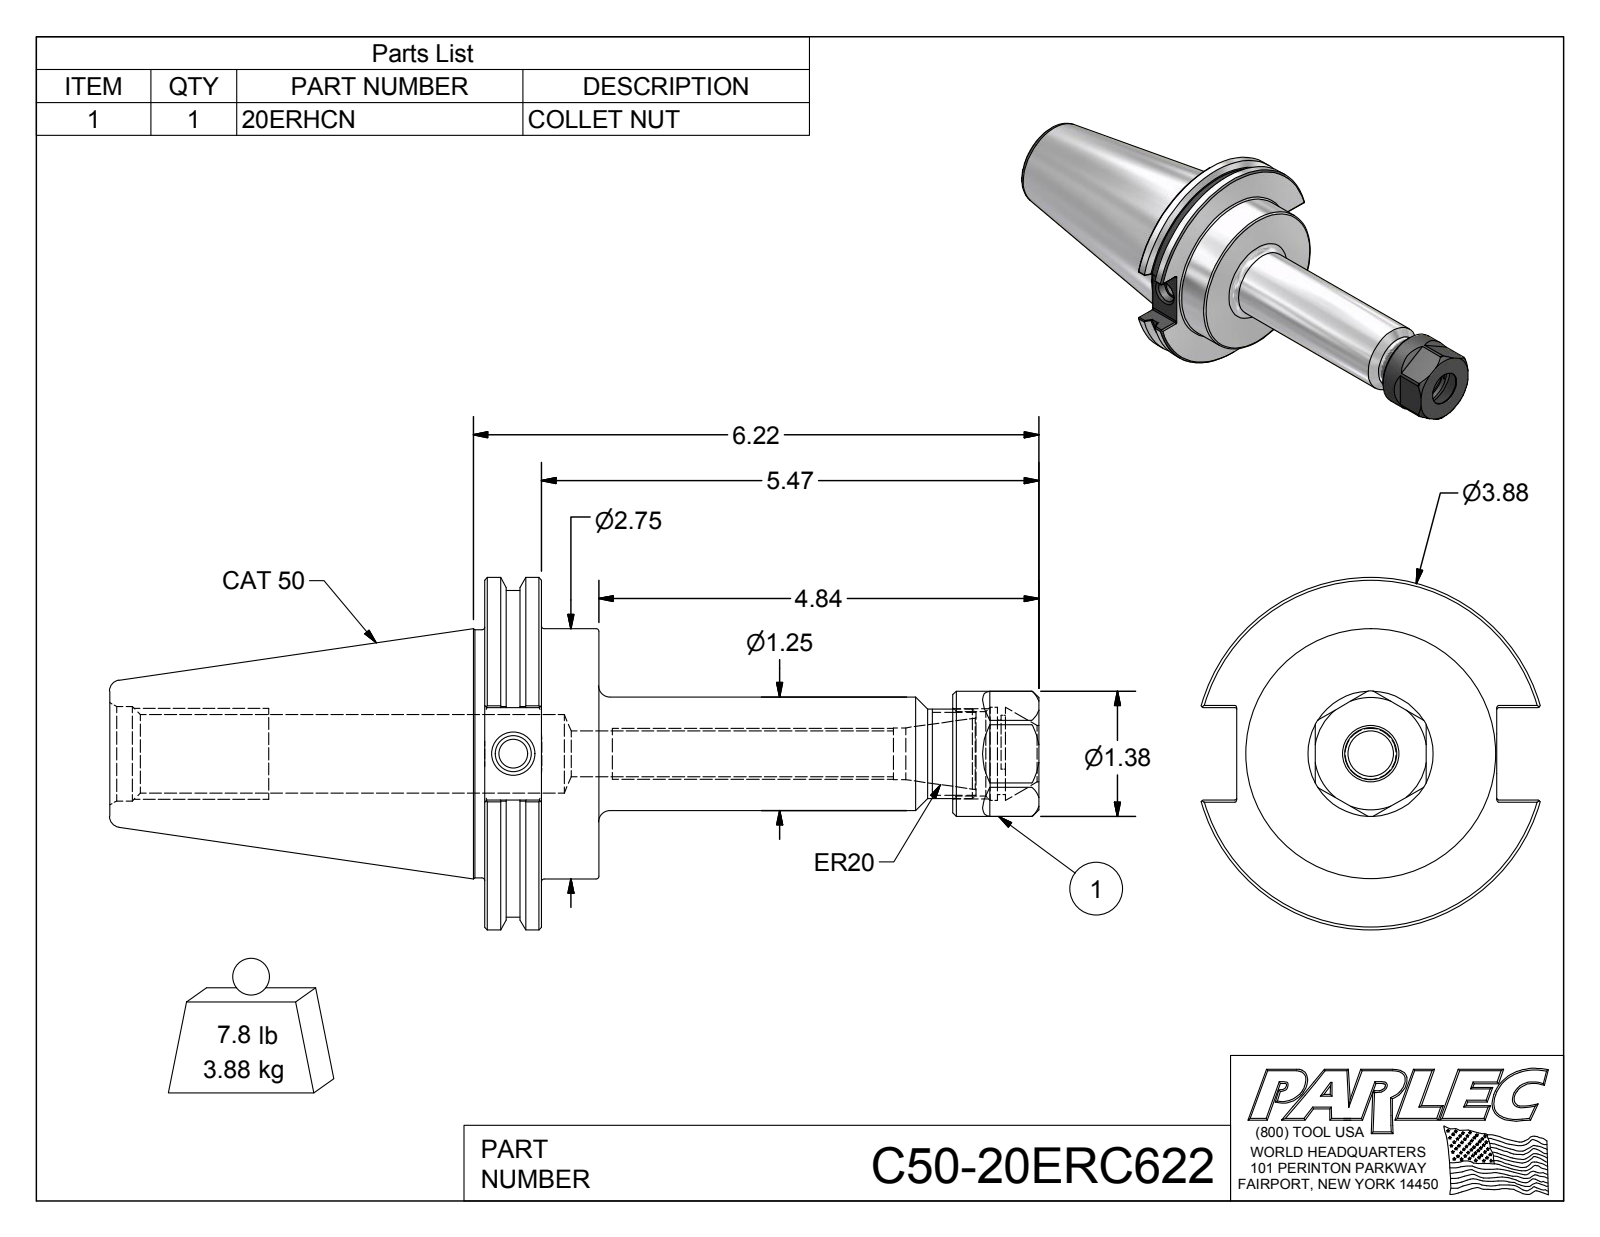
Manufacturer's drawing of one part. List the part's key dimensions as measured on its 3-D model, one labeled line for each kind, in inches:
Part name (STEP PRODUCT): C50-20ERC622; C50-20ER6-1; 20ERHCN
STEP written by: Autodesk Inventor 2012 (AUTOMOTIVE_DESIGN)
Units: inches
Bodies: 2 solids, 132 faces (50 planar, 34 cylindrical, 48 other)
Overall size (bounding box): 10.22 × 3.875 × 3.729
Volume: 27.44 in³ · Surface area: 106.3 in²
Round holes (diameter × count): ⌀0.315 ×1, ⌀0.399 ×1, ⌀0.502 ×1, ⌀0.57 ×1, ⌀0.62 ×1, ⌀0.82 ×1, ⌀0.865 ×1, ⌀0.925 ×1, ⌀1.024 ×1, ⌀1.038 ×1
Round bosses / shafts (diameter × count): ⌀3.875 ×1, ⌀3.594 ×1, ⌀2.75 ×1, ⌀2.73 ×1, ⌀1.378 ×1, ⌀1.25 ×1, ⌀0.984 ×1
Partial cylindrical surfaces — rounded edges, fillets, slot ends (radius × count): R0.02 ×12, R0.423 ×1
Main face-to-face distances: 0.625, 1.255, 0.63, 1.22, 6.095, 5.47, 4.84, 5.15, 4.525, 3.895
Hole centre spacings: 0.037
